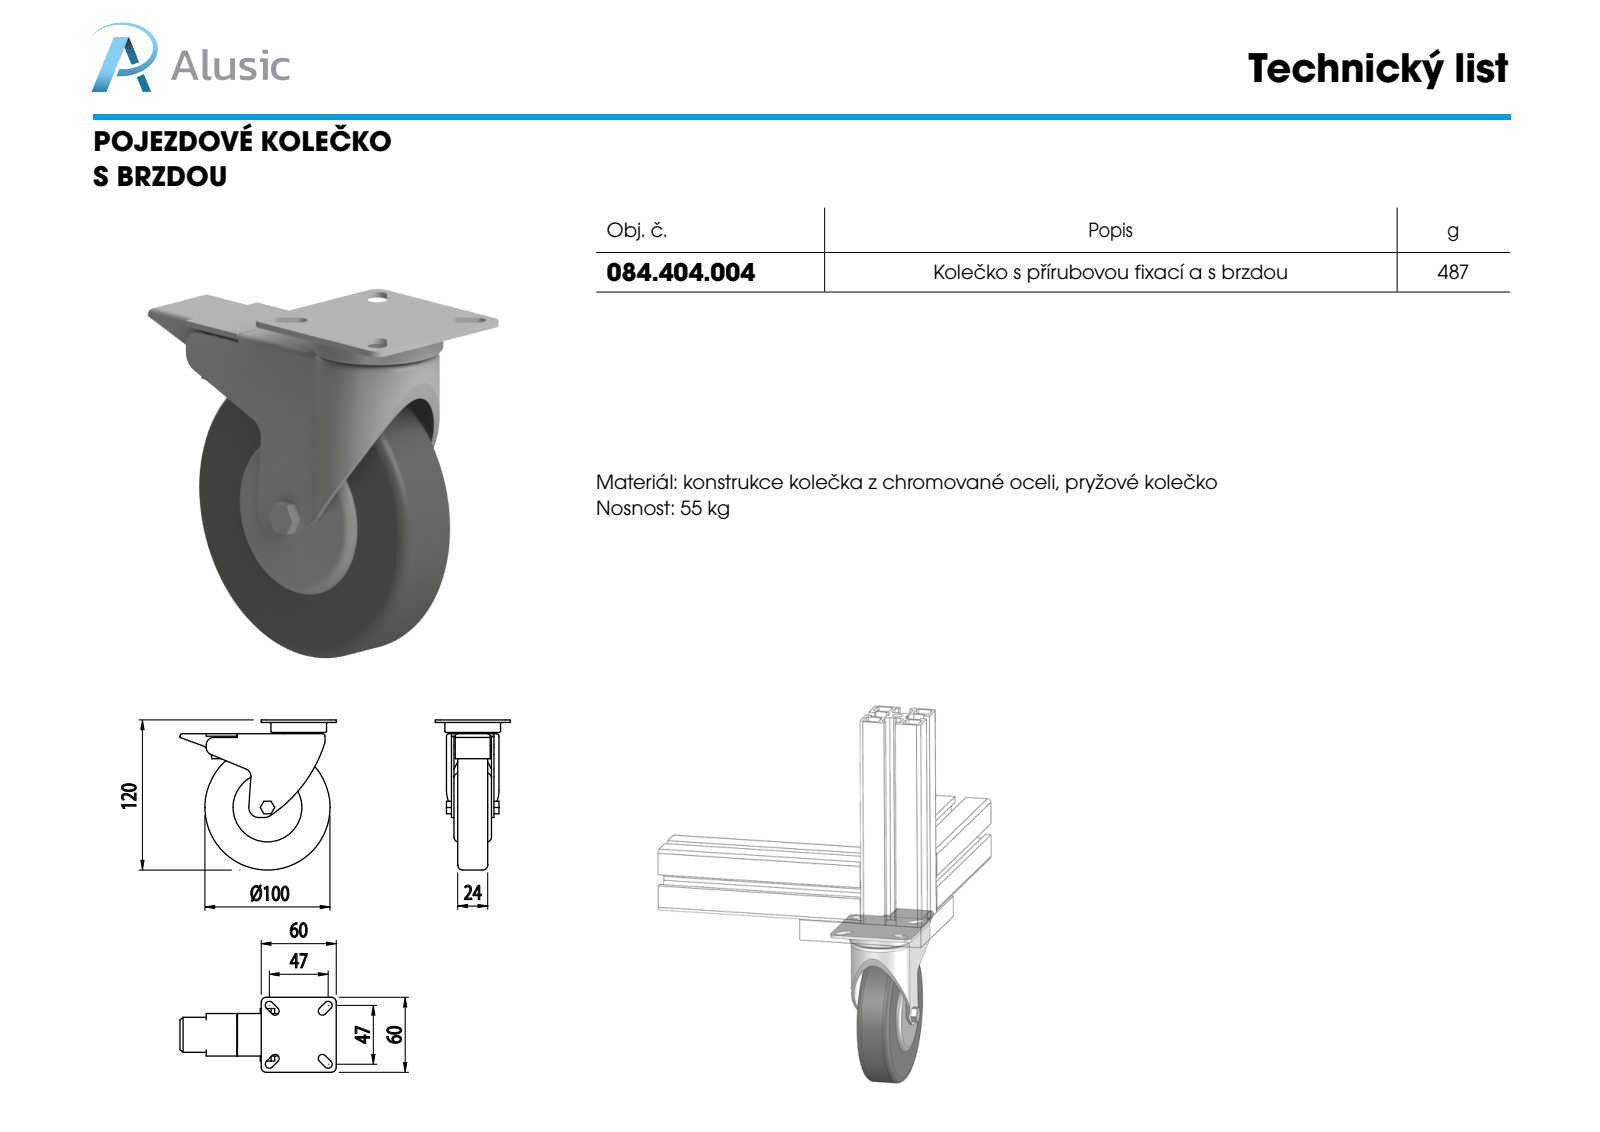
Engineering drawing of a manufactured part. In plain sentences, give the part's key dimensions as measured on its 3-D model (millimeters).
The part is named "084.404.004". Its 3-D file was written by "SolidWorks 2011 (CONFIG_CONTROL_DESIGN)". It is 8 solids with 134 faces: 72 planar, 47 cylindrical and 15 other. Overall it measures 125 by 120 by 60 millimeters. Its volume is 249 625 cubic millimeters and its surface area 66 535 square millimeters. Round bosses or shafts: 1 of diameter 100, 1 of diameter 44.5. Partial cylindrical surfaces (rounded edges, fillets, slot ends): 8 of radius 3.25, 5 of radius 2, 4 of radius 4, 4 of radius 8, 3 of radius 6, 2 of radius 10, 1 of radius 12, 1 of radius 19. The main face-to-face distances are 3, 2, 24, 27, 29, 11, 32, 5, 30, 1.
